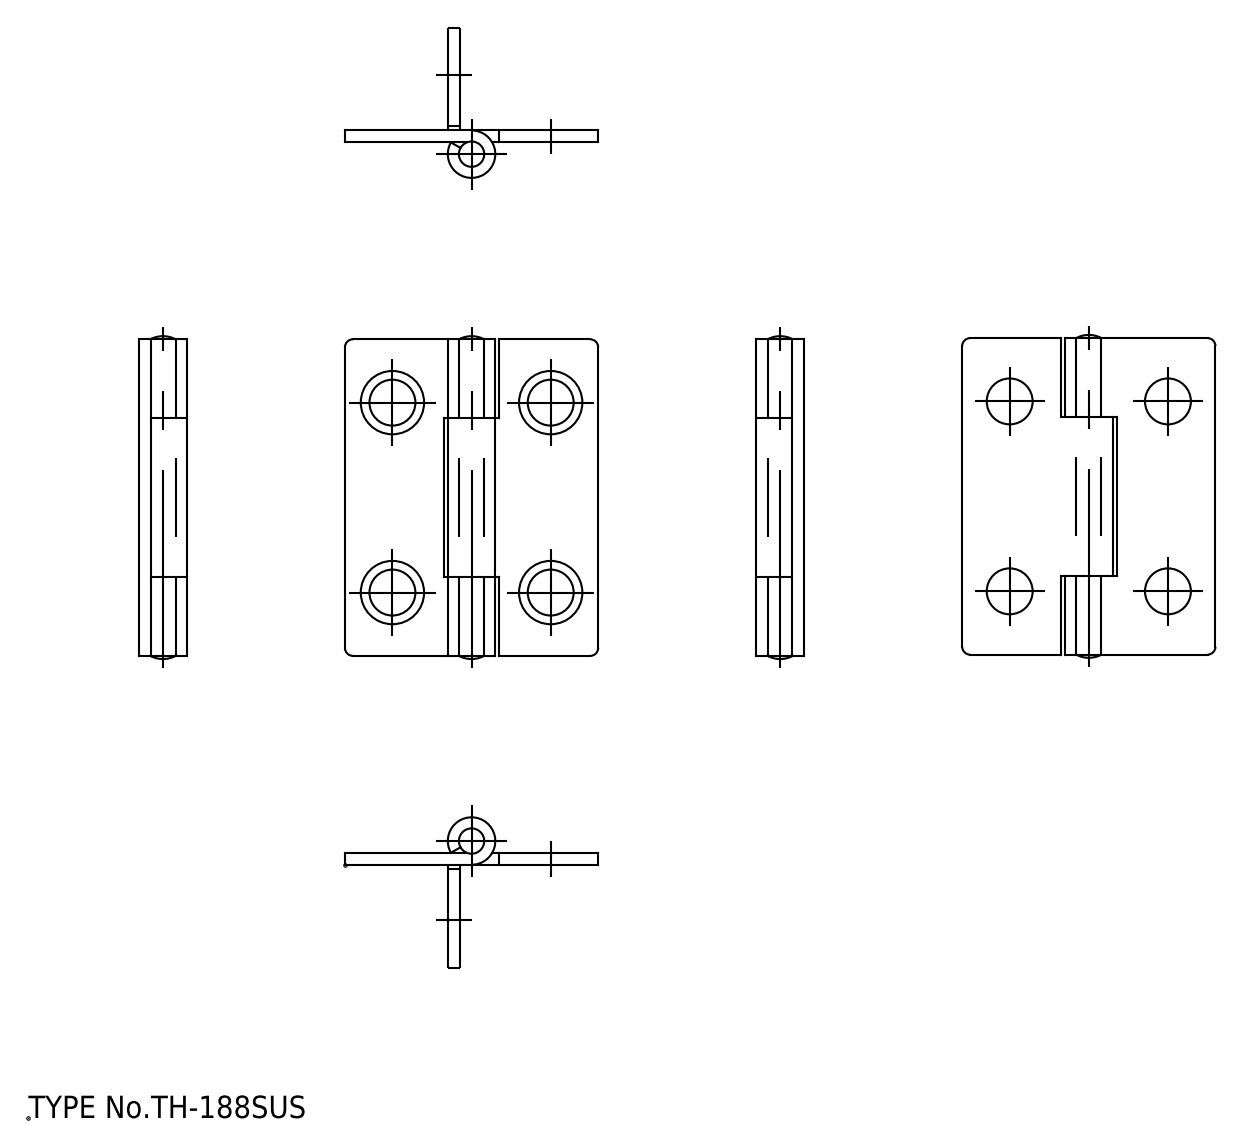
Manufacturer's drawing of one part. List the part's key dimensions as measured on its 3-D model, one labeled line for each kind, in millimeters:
Part name (STEP PRODUCT): TH_188SUS_1; TH_188SUS_2; TH_188SUS_3
STEP written by: spGate 19.8.4 (****-****-****-****) (AUTOMOTIVE_DESIGN)
Units: millimetres
Bodies: 3 solids, 54 faces (22 planar, 20 cylindrical, 12 other)
Overall size (bounding box): 40.8 × 32 × 6
Volume: 2 492 mm³ · Surface area: 3 922 mm²
Round holes (diameter × count): ⌀5.8 ×4, ⌀3 ×1
Round bosses / shafts (diameter × count): ⌀6 ×1
Partial cylindrical surfaces — rounded edges, fillets, slot ends (radius × count): R1 ×4
Main face-to-face distances: 1.5, 10, 30, 12.5, 19.5, 40, 32, 20, 7
Hole centre spacings: 20, 24, 31.24
